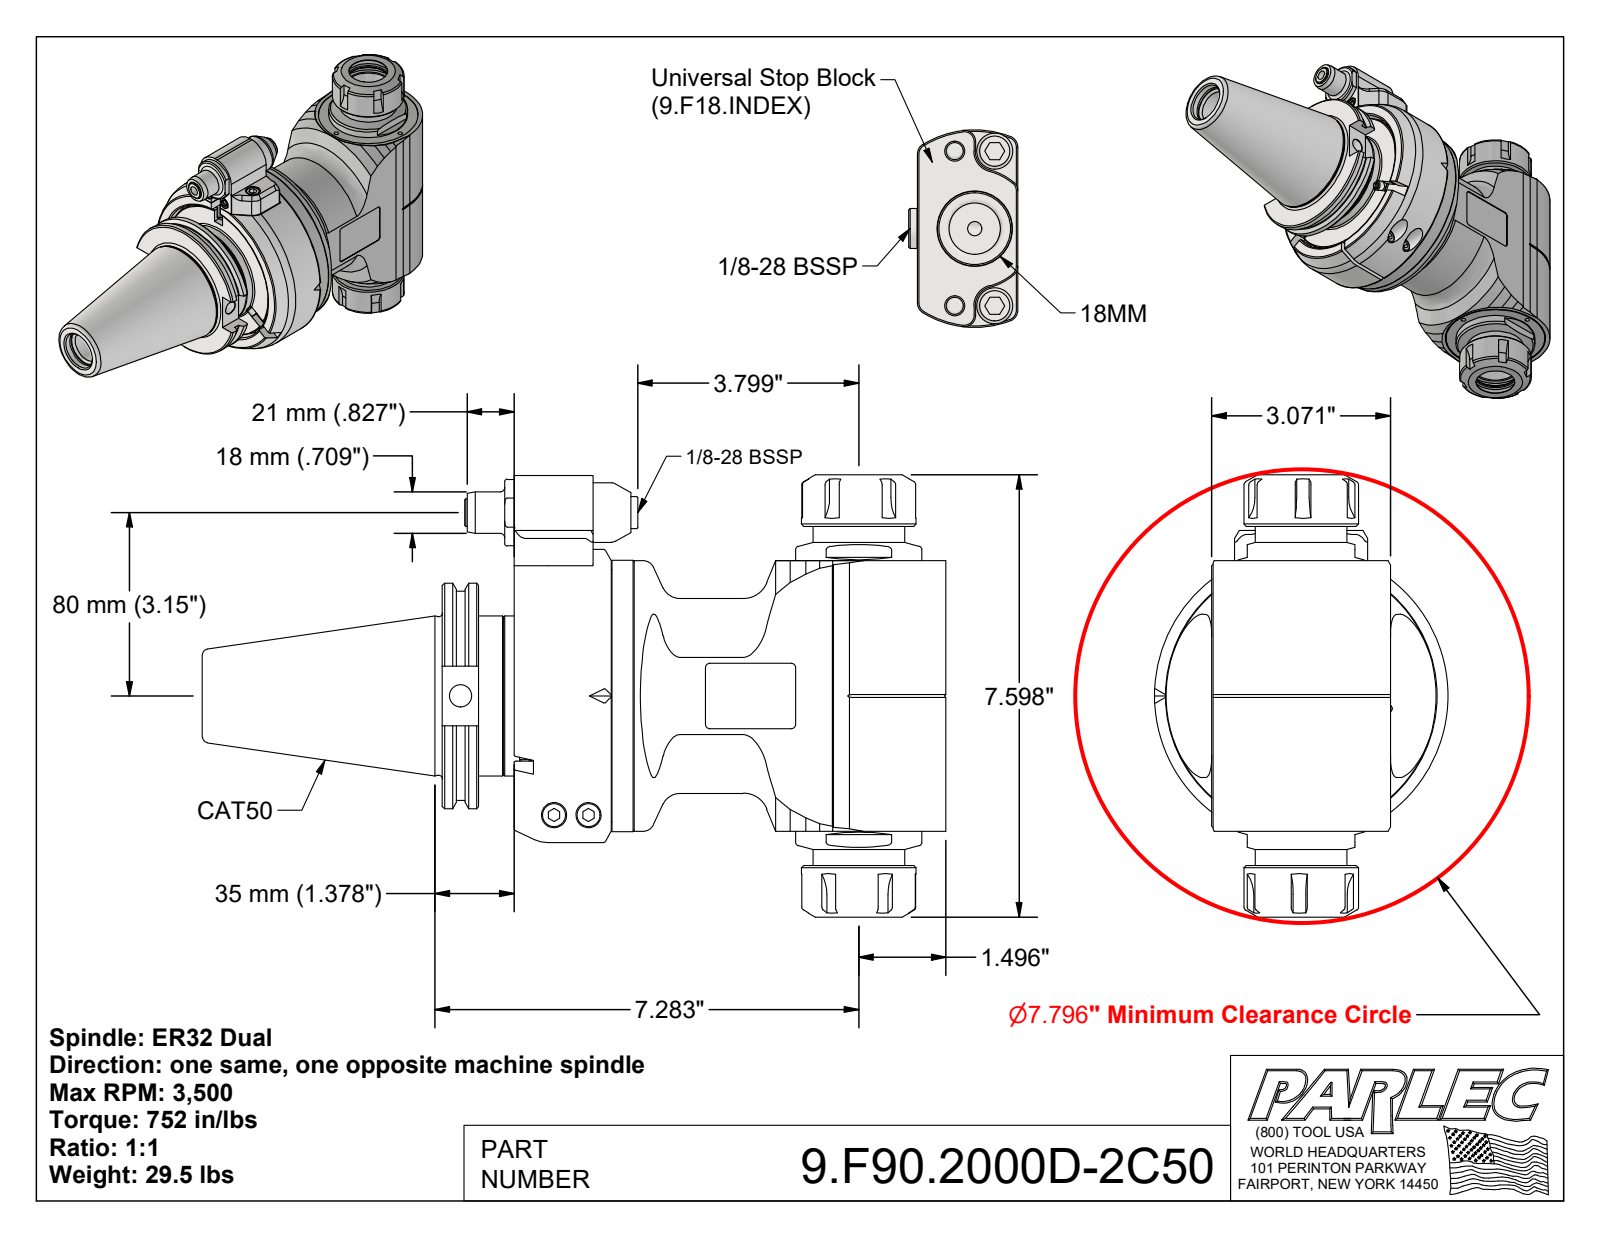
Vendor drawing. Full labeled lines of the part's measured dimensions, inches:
Part name (STEP PRODUCT): 9.F90.2000D-2C50; F90-20D; 9_GA2_458_2 (Type 2, Cat50, 80mm)
STEP written by: Autodesk Inventor 2022 (AUTOMOTIVE_DESIGN)
Units: inches
Bodies: 5 solids, 674 faces (284 planar, 168 cylindrical, 222 other)
Overall size (bounding box): 12.78 × 7.598 × 5.039
Volume: 127.9 in³ · Surface area: 369.8 in²
Round holes (diameter × count): ⌀0.413 ×20, ⌀0.126 ×4, ⌀0.197 ×4, ⌀0.102 ×2, ⌀0.165 ×2, ⌀0.209 ×2, ⌀0.315 ×2, ⌀0.409 ×2, ⌀0.433 ×2, ⌀0.492 ×2, ⌀1.063 ×2, ⌀0.098 ×1
Round bosses / shafts (diameter × count): ⌀0.394 ×4, ⌀0.236 ×4, ⌀0.709 ×2, ⌀0.098 ×2, ⌀5.039 ×1, ⌀4.665 ×1, ⌀4.646 ×1, ⌀3.898 ×1
Partial cylindrical surfaces — rounded edges, fillets, slot ends (radius × count): R0.079 ×12, R0.591 ×12, R0.157 ×4, R0.016 ×2, R0.02 ×2, R0.039 ×2, R0.138 ×2, R0.315 ×2
Main face-to-face distances: 1.378, 1.575, 0.236, 1.339, 3.071, 0.197, 0.039, 0.335, 0.02, 2.281
Hole centre spacings: 1.841, 3.645, 1.785, 2.215, 2.603, 2.603, 3.22, 3.539
